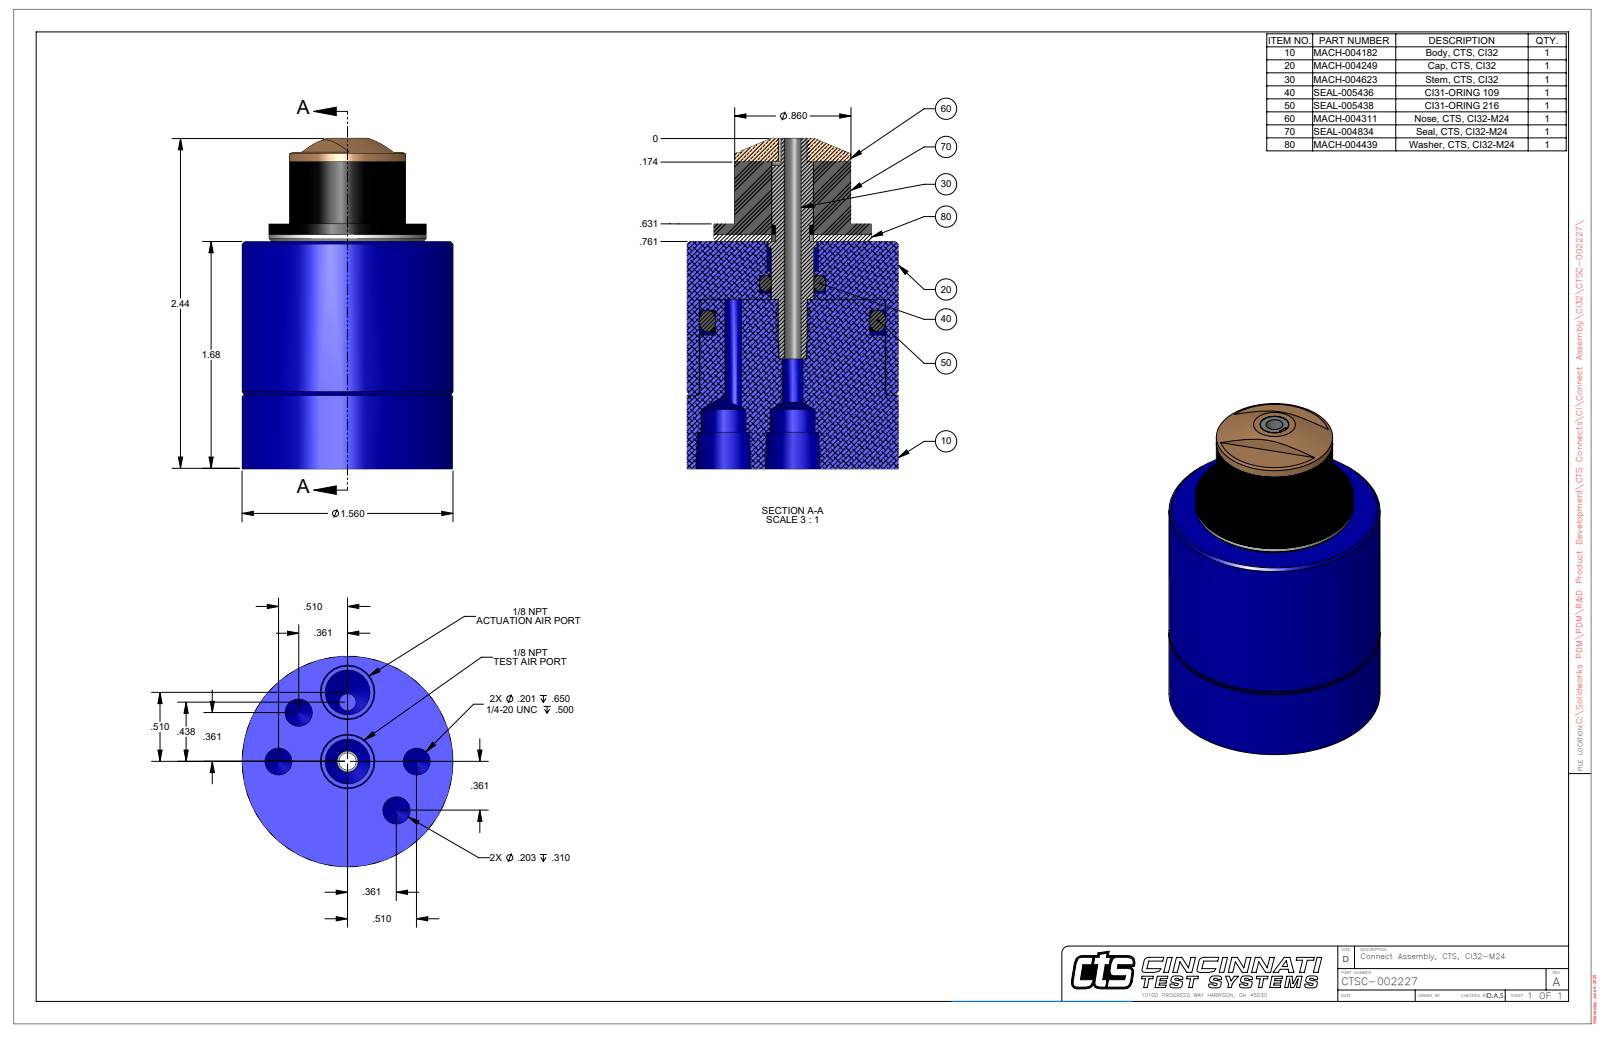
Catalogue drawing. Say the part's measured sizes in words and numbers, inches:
The part is named "CTSC-002227". Its 3-D file was written by "SolidWorks 2023 (AUTOMOTIVE_DESIGN)". It is 1 solid with 103 faces: 29 planar, 40 cylindrical and 34 other. Overall it measures 2.438 by 1.56 by 1.56 inches. Its volume is 3.462 cubic inches and its surface area 19.96 square inches. Round holes: 2 of diameter 0.125, 2 of diameter 0.201, 2 of diameter 0.203, 2 of diameter 0.332, 1 of diameter 0.156, 1 of diameter 0.213, 1 of diameter 0.314, 1 of diameter 0.38, 1 of diameter 1.377. Round bosses or shafts: 1 of diameter 1.56, 1 of diameter 1.365, 1 of diameter 1.165, 1 of diameter 0.86, 1 of diameter 0.357, 1 of diameter 0.31. The main face-to-face distances are 1.677, 1.807, 0.13, 2.334, 0.657, 0.527, 0.542, 1.135, 1.265, 1.792. The hole center spacings are 0.51, 0.39, 0.942, 0.672, 0.721, 0.072, 0.369, 0.437.
